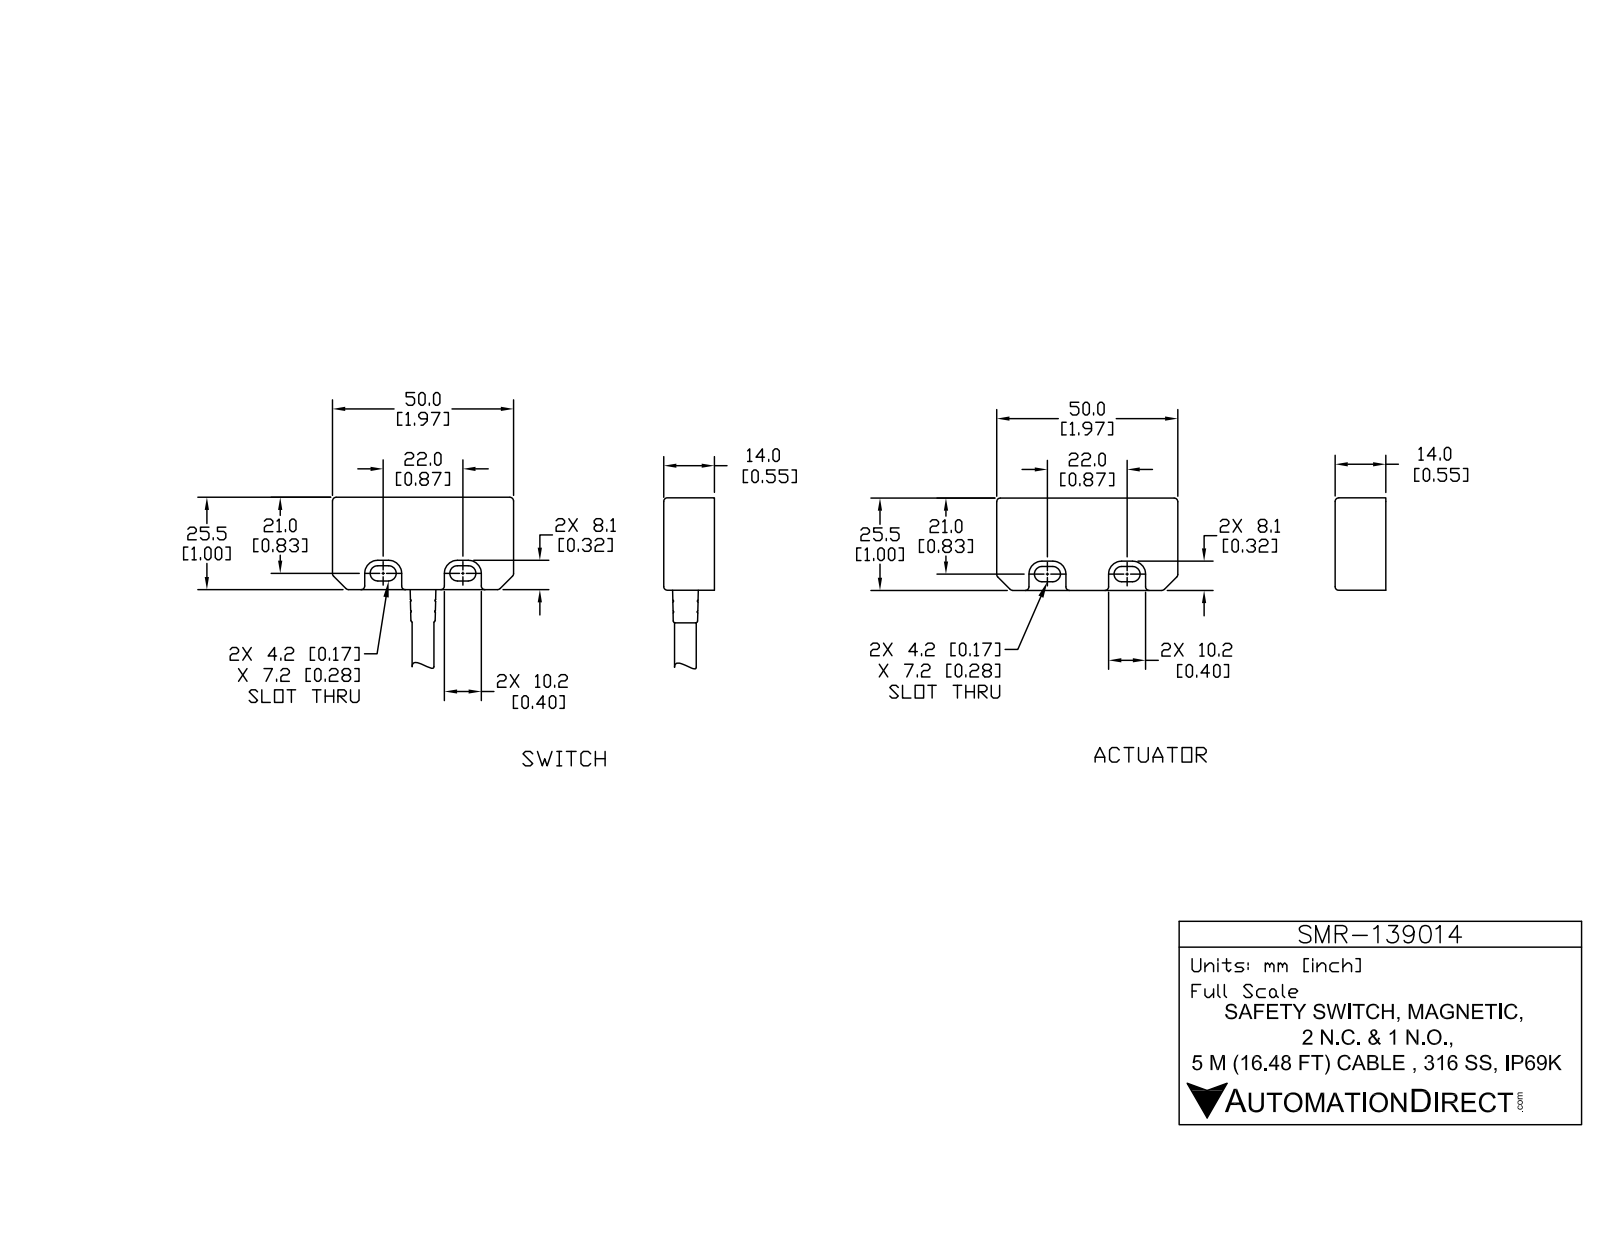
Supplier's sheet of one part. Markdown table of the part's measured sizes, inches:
| quantity | value |
| --- | --- |
| part name | SMR-139014_2; SMR-139014_1; SMR-139014 |
| STEP written by | SolidWorks 2017 (AUTOMOTIVE_DESIGN) |
| units | inches |
| bodies | 4 solids, 201 faces (45 planar, 88 cylindrical, 68 other) |
| overall size | 6.063 × 1.969 × 0.551 |
| volume | 2.184 in³ |
| surface area | 18.53 in² |
| round holes (diameter × count) | 0.287 × 1 |
| round bosses / shafts (diameter × count) | 0.236 × 1 |
| partial cylindrical surfaces (radius × count) | 0.039 × 38, 0.083 × 8, 0.142 × 8, 0.02 × 6 |
| main face-to-face distances | 0.551, 1.004, 1.043, 0.039, 1.969, 2.047, 2.617, 0.177, 0.374, 0.26 |
